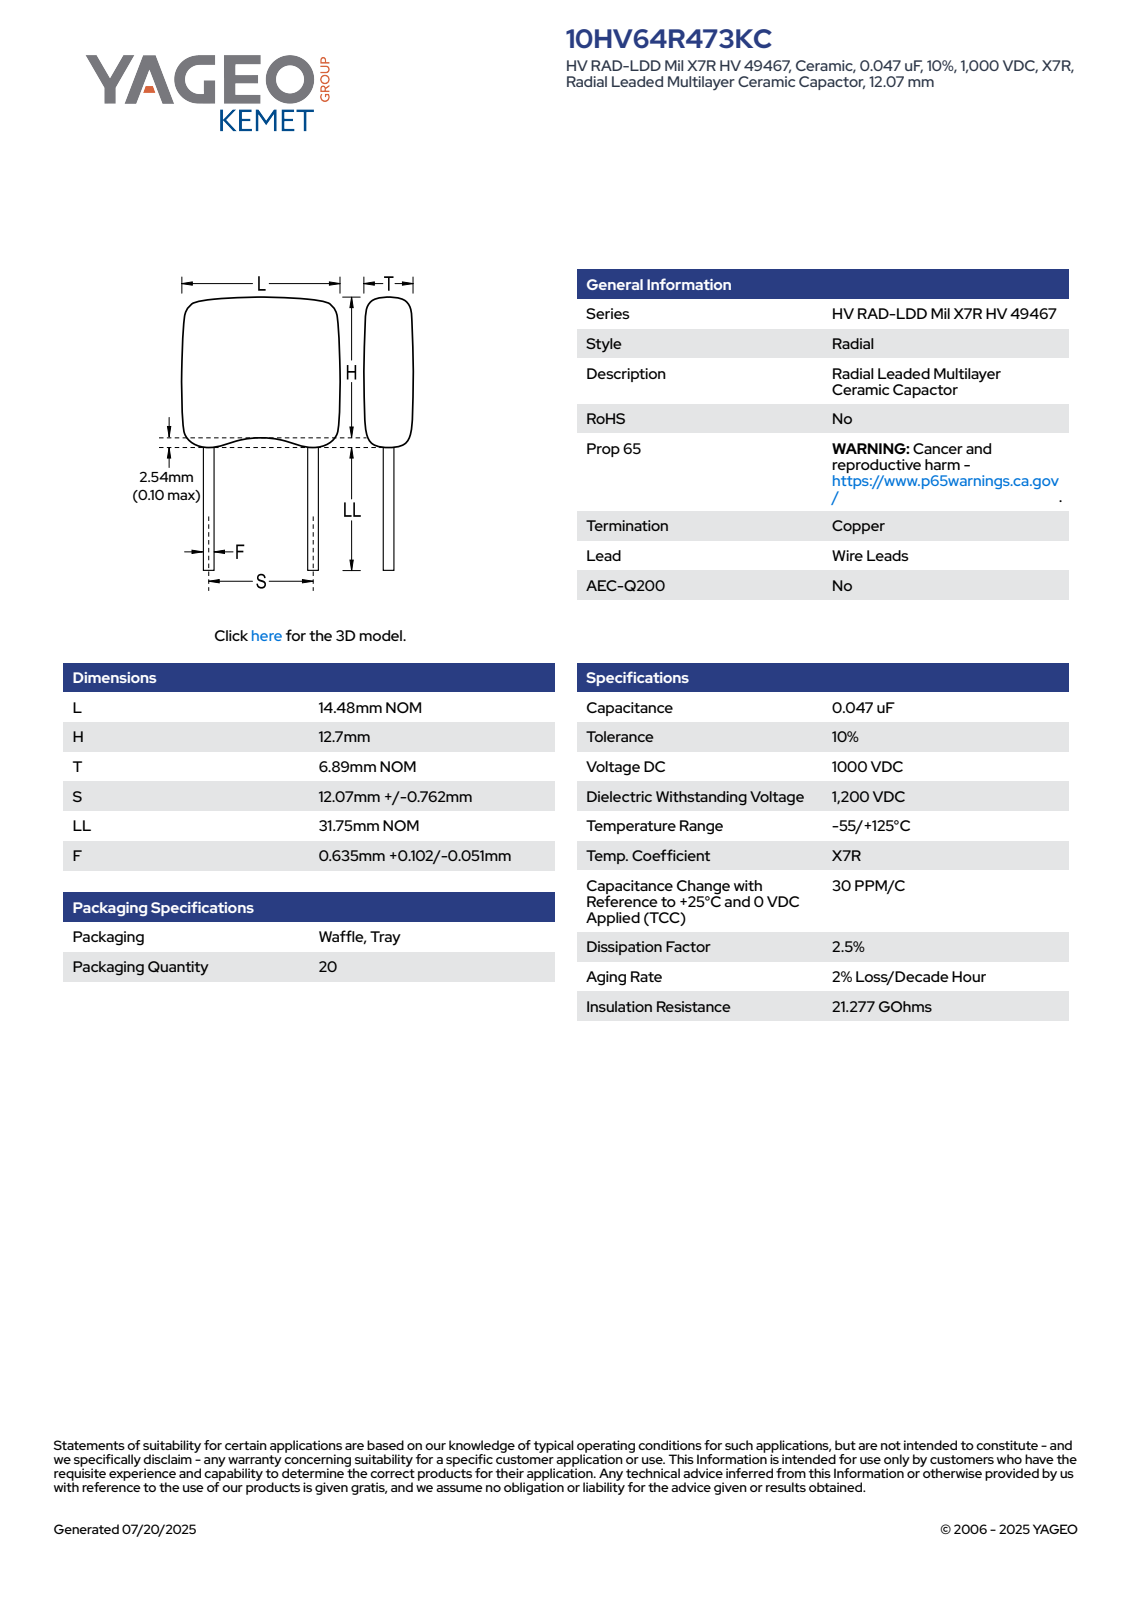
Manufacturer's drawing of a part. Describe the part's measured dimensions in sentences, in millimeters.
The part is named "CCRM_RCST_HV64_L14.48H12.7T6.89S12.07LL31.75F0.737". Its 3-D file was written by "SolidWorks 2021 (AUTOMOTIVE_DESIGN)". It is 4 solids with 98 faces: 66 planar, 20 cylindrical and 12 other. Overall it measures 17.45 by 14.48 by 6.89 millimeters. Its volume is 1 308 cubic millimeters and its surface area 774 square millimeters. Round bosses or shafts: 2 of diameter 0.74. Partial cylindrical surfaces (rounded edges, fillets, slot ends): 8 of radius 1, 4 of radius 0.5. The main face-to-face distances are 6.89, 14.48, 14.28, 3.17, 17.45, 11.34, 8.17, 6.11, 9.5, 6.33.
